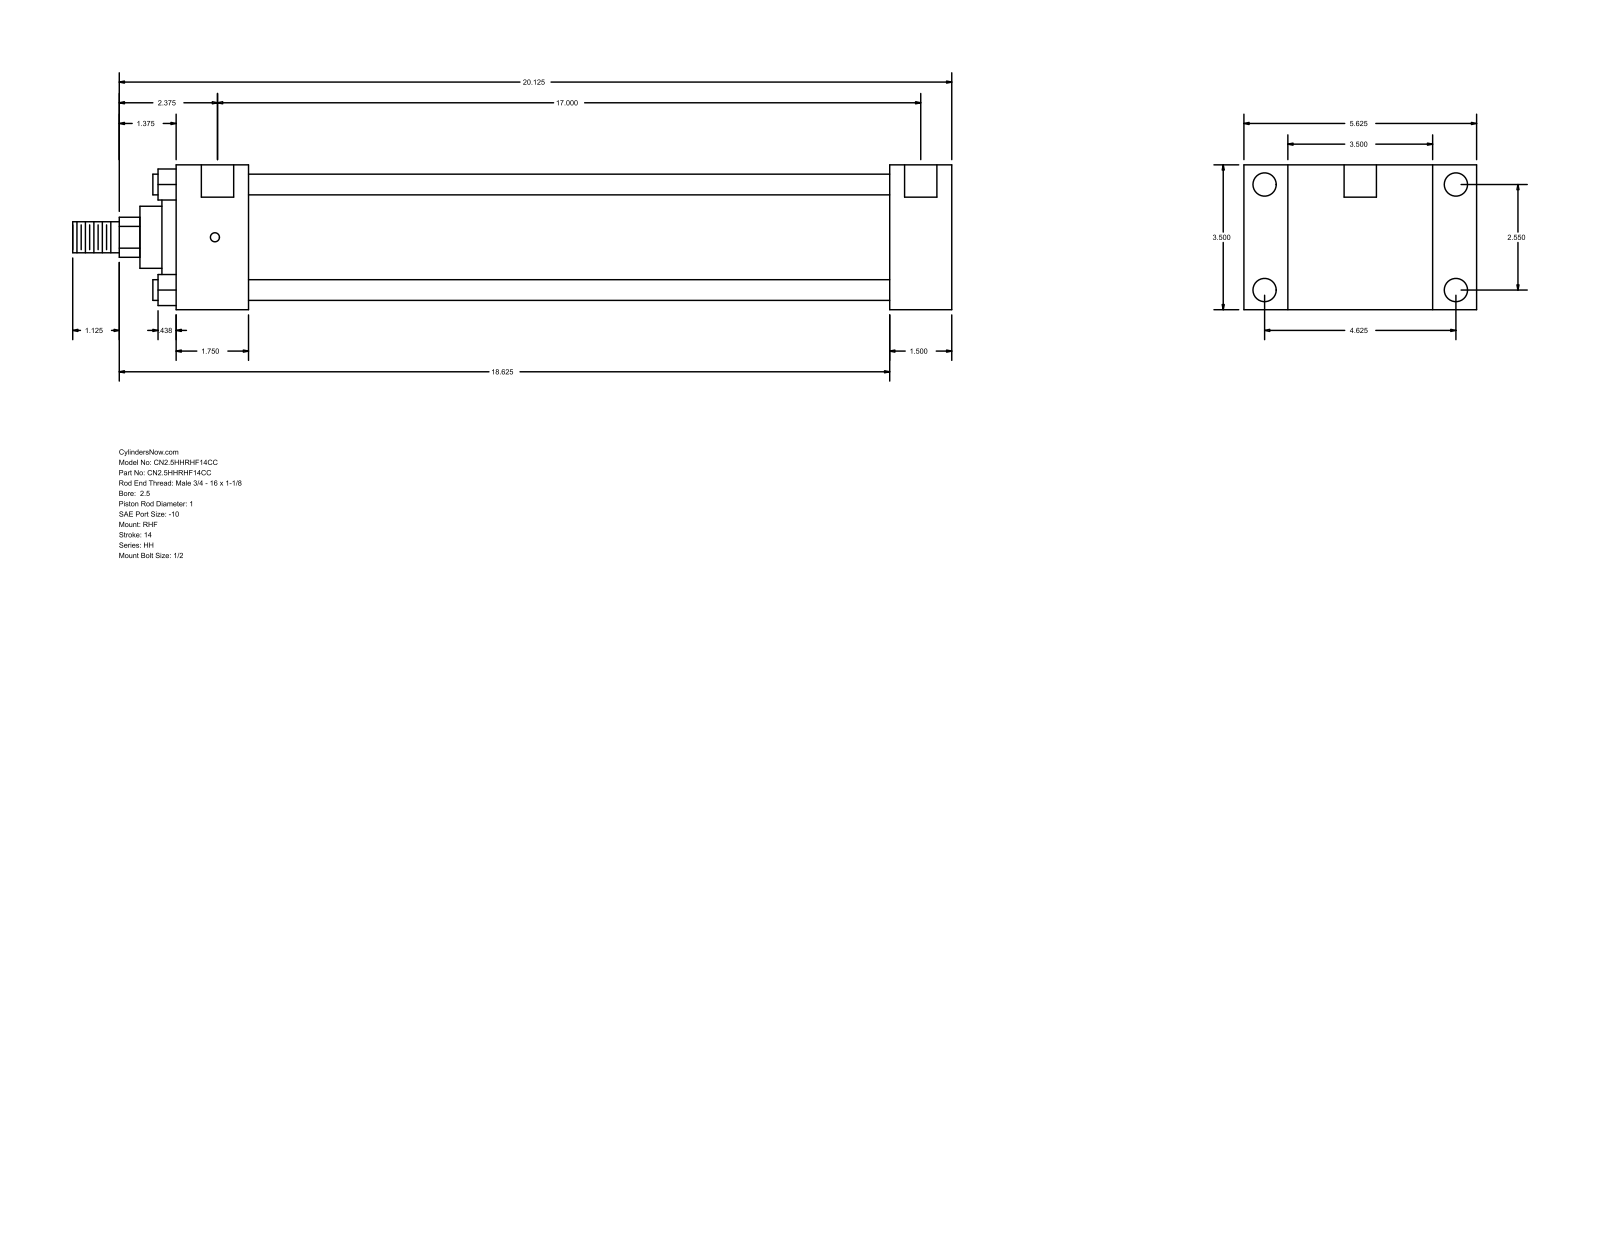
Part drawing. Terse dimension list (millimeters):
name: HH_RHF__0250_1
written by: GSSL Pune (CONFIG_CONTROL_DESIGN)
unit: mm
bodies: 0 solids, 90 faces (61 planar, 29 cylindrical, 0 other)
size: 539.75 × 142.88 × 88.9
holes: 4× ⌀5.56, 4× ⌀14.3, 2× ⌀19.84
bosses: 4× ⌀12.7, 1× ⌀73.03, 1× ⌀60.33, 1× ⌀38.1, 1× ⌀25.4, 1× ⌀19.05
rounds: 1× R12.29
face distances: 88.9, 38.11, 26.99, 115.89, 438.15, 476.26, 142.88, 44.46, 393.69, 431.8
hole spacings: 1.59, 64.76, 117.48, 134.15, 433.38, 434.97, 431.79
